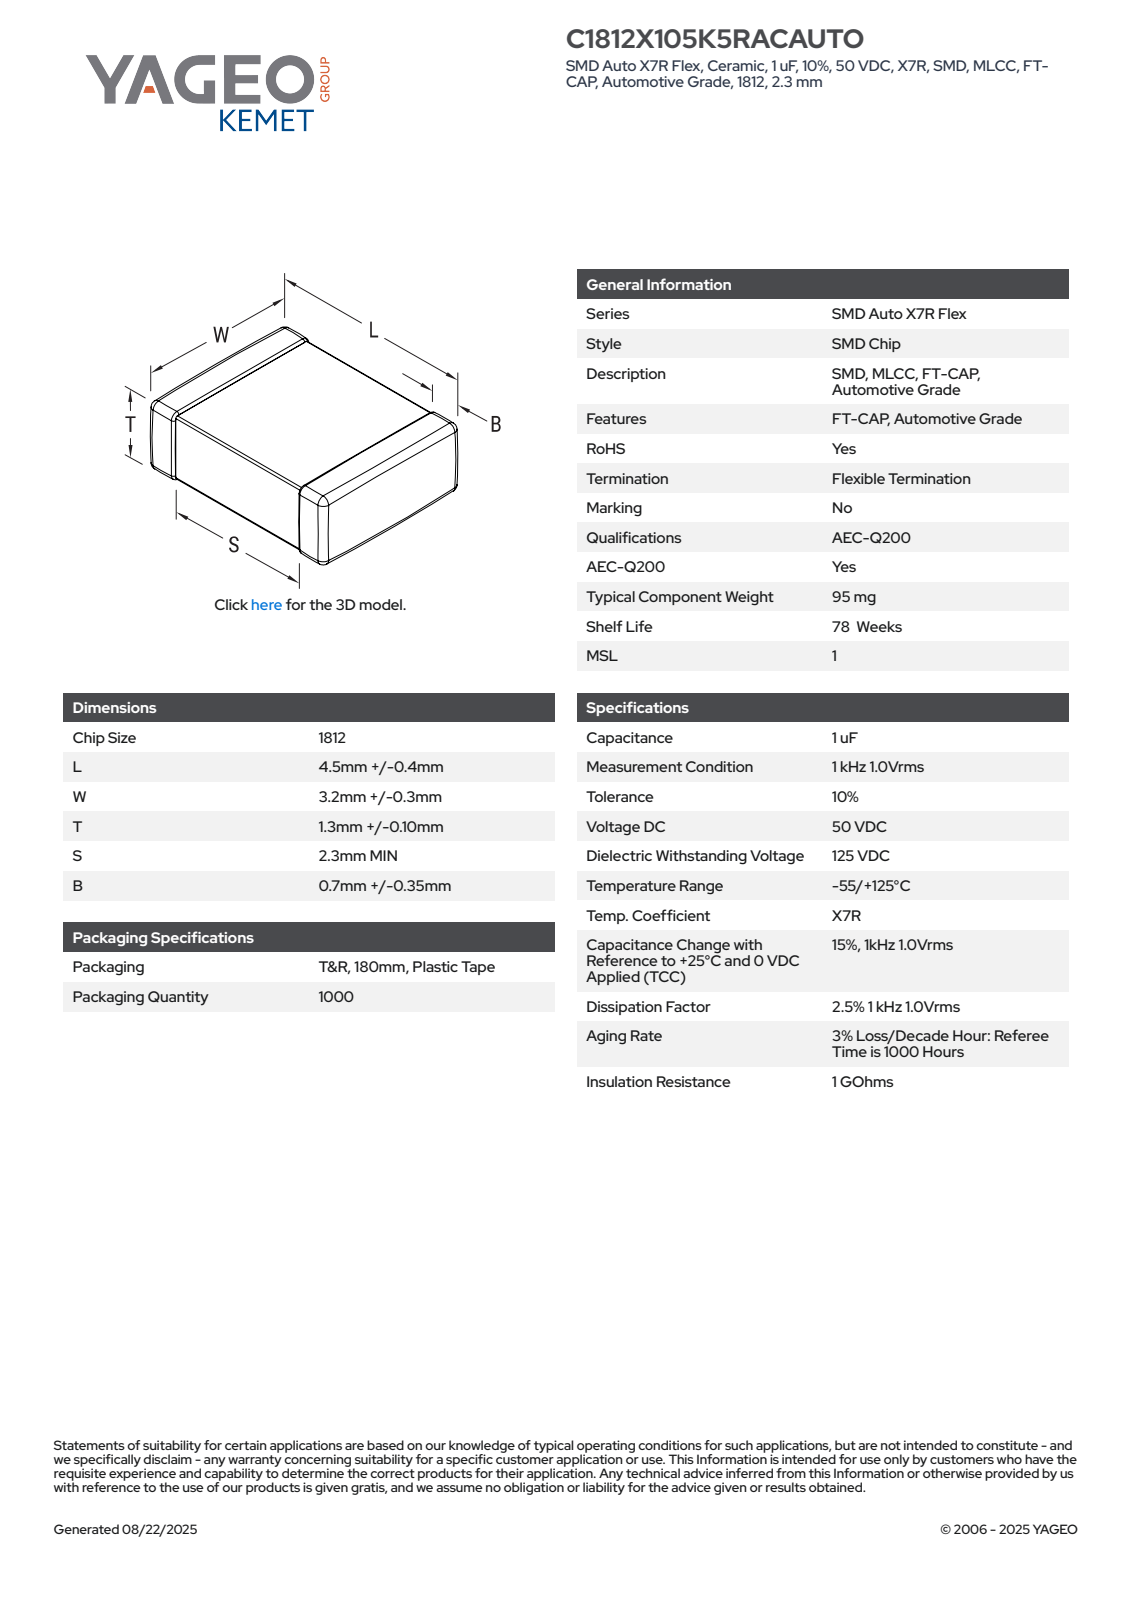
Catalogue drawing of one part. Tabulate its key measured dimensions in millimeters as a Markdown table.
| quantity | value |
| --- | --- |
| part name | CCS_CCSTD_1812_L4.9W3.5T1.4B0.7 |
| STEP written by | SolidWorks 2021 (AUTOMOTIVE_DESIGN) |
| units | millimeters |
| bodies | 4 solids, 125 faces (71 planar, 38 cylindrical, 16 other) |
| overall size | 4.9 × 3.5 × 1.4 |
| volume | 22 mm³ |
| surface area | 57 mm² |
| main face-to-face distances | 1.33, 1.26, 1.4, 3.43, 4.9, 3.36, 3.5, 0.52, 2.25, 2.13 |
